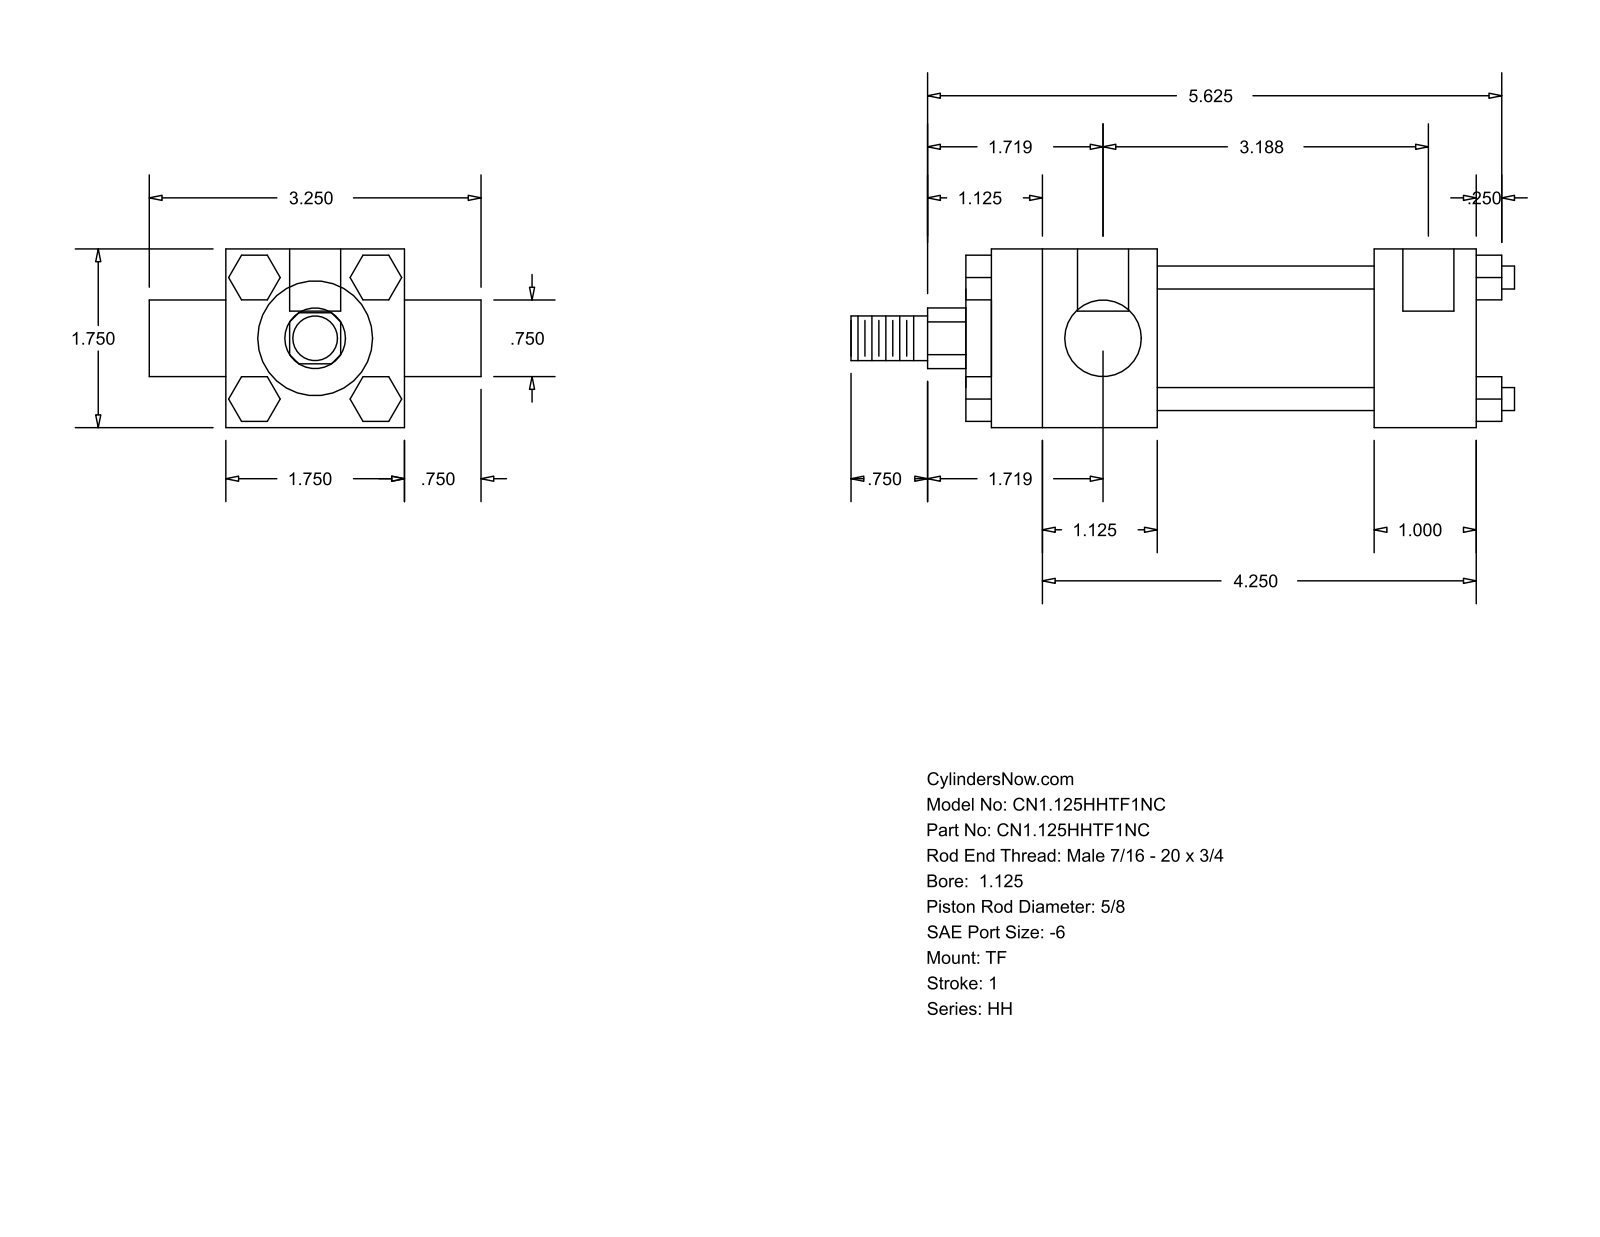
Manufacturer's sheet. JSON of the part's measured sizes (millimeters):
{"part_name": "HH_TF__0112_0.625", "step_written_by": "GSSL Pune (CONFIG_CONTROL_DESIGN)", "units": "millimeters", "bodies": {"solids": 0, "faces": 120, "planar": 92, "cylindrical": 28, "other": 0}, "overall_size": [165.1, 82.55, 44.45], "round_holes": [[5.56, 3], [12.7, 2]], "round_bosses_or_shafts": [[5.71, 4], [34.92, 1], [28.57, 1], [19.05, 1], [15.88, 1], [11.11, 1]], "partial_cylinders_radius": [[7.54, 1]], "face_to_face_distances": [44.46, 6.35, 127, 11.11, 53.97, 79.38, 25.41, 41.27, 95.24, 120.65], "hole_center_spacings": [3.17, 77.79, 80.96]}
